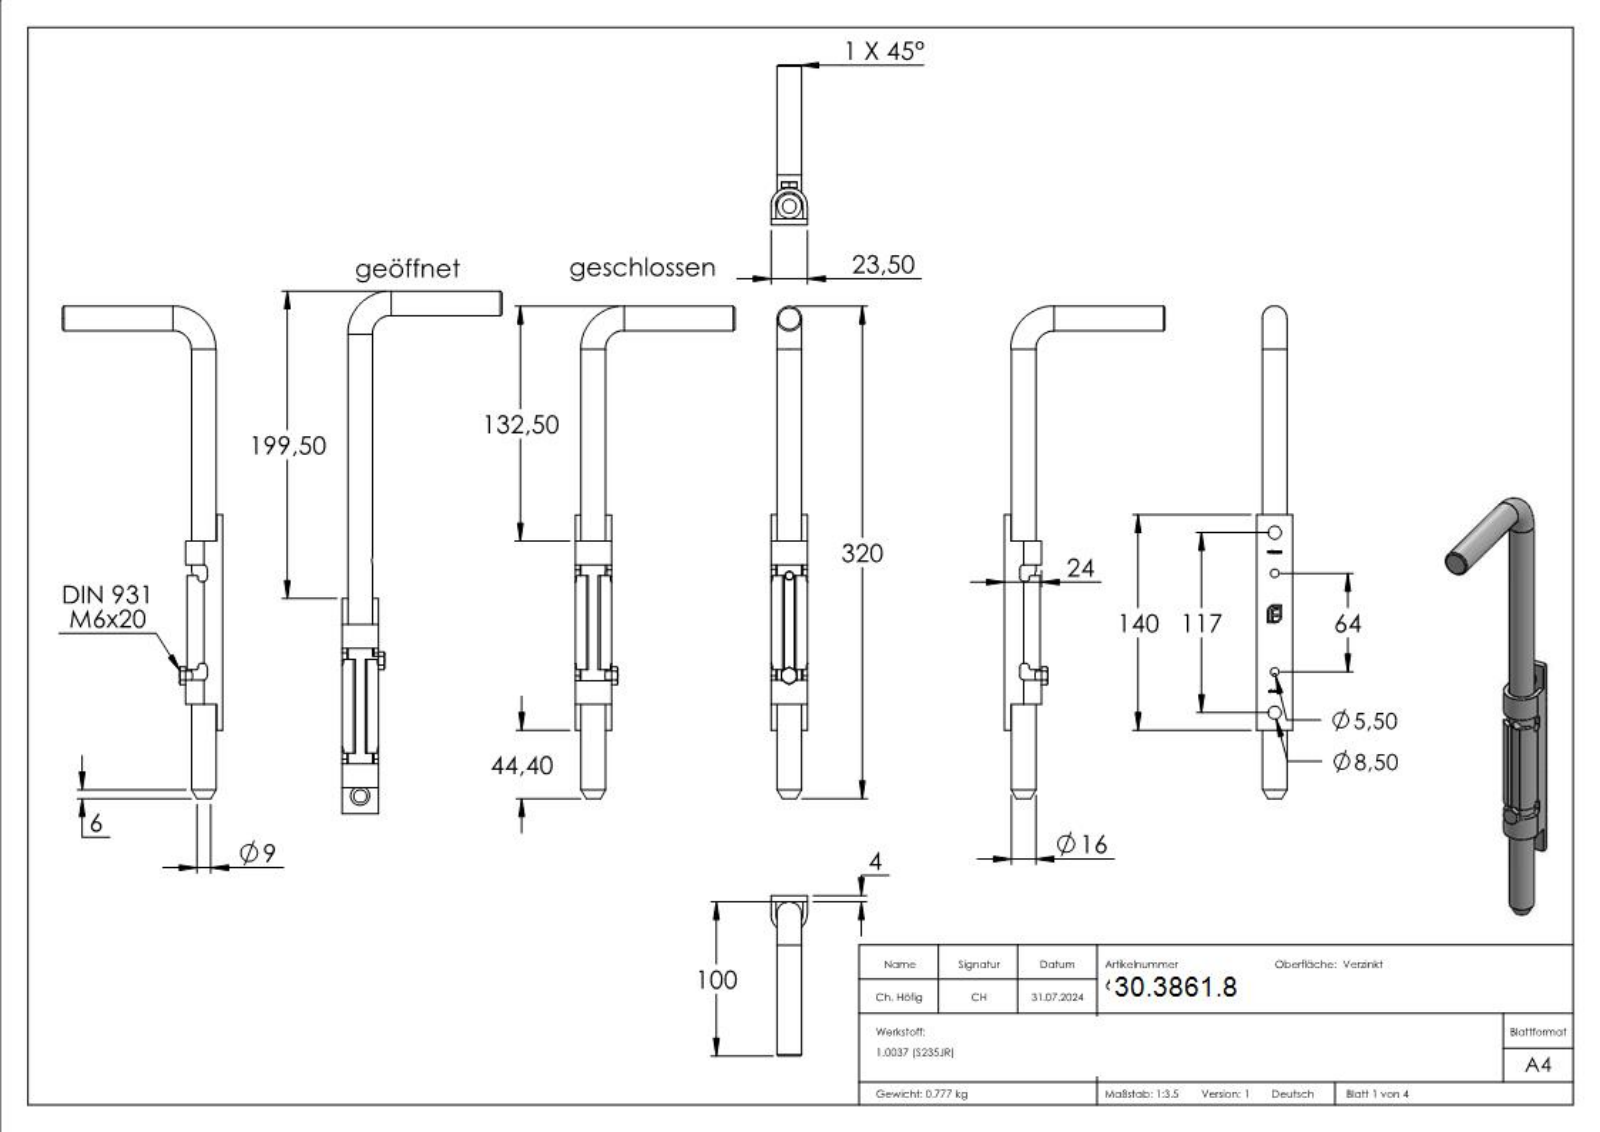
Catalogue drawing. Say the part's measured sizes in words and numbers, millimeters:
The part is named "67-A-X00 Teil1_67-A-300 Teil1; DIN 931_DIN 931 M6x20; 67-A-X00 Teil2_67-A-300 Teil2; 67-A-300". Its 3-D file was written by "SolidWorks 2018 (CONFIG_CONTROL_DESIGN)". It is 3 solids with 332 faces: 172 planar, 33 cylindrical and 127 other. Overall it measures 320 by 104.25 by 23.5 millimeters. Its volume is 104 028 cubic millimeters and its surface area 37 677 square millimeters. Round holes: 2 of diameter 5, 2 of diameter 5.5, 2 of diameter 8.5. Round bosses or shafts: 2 of diameter 16, 1 of diameter 6. Partial cylindrical surfaces (rounded edges, fillets, slot ends): 4 of radius 3, 2 of radius 1, 2 of radius 2, 1 of radius 8.75, 1 of radius 11.75. The main face-to-face distances are 4, 3, 20.5, 23.5, 17.5, 17, 123, 32.5, 107.5, 15.5. The hole center spacings are 26.5, 90.5, 1.5, 2.5, 24, 28, 62.5, 64.
